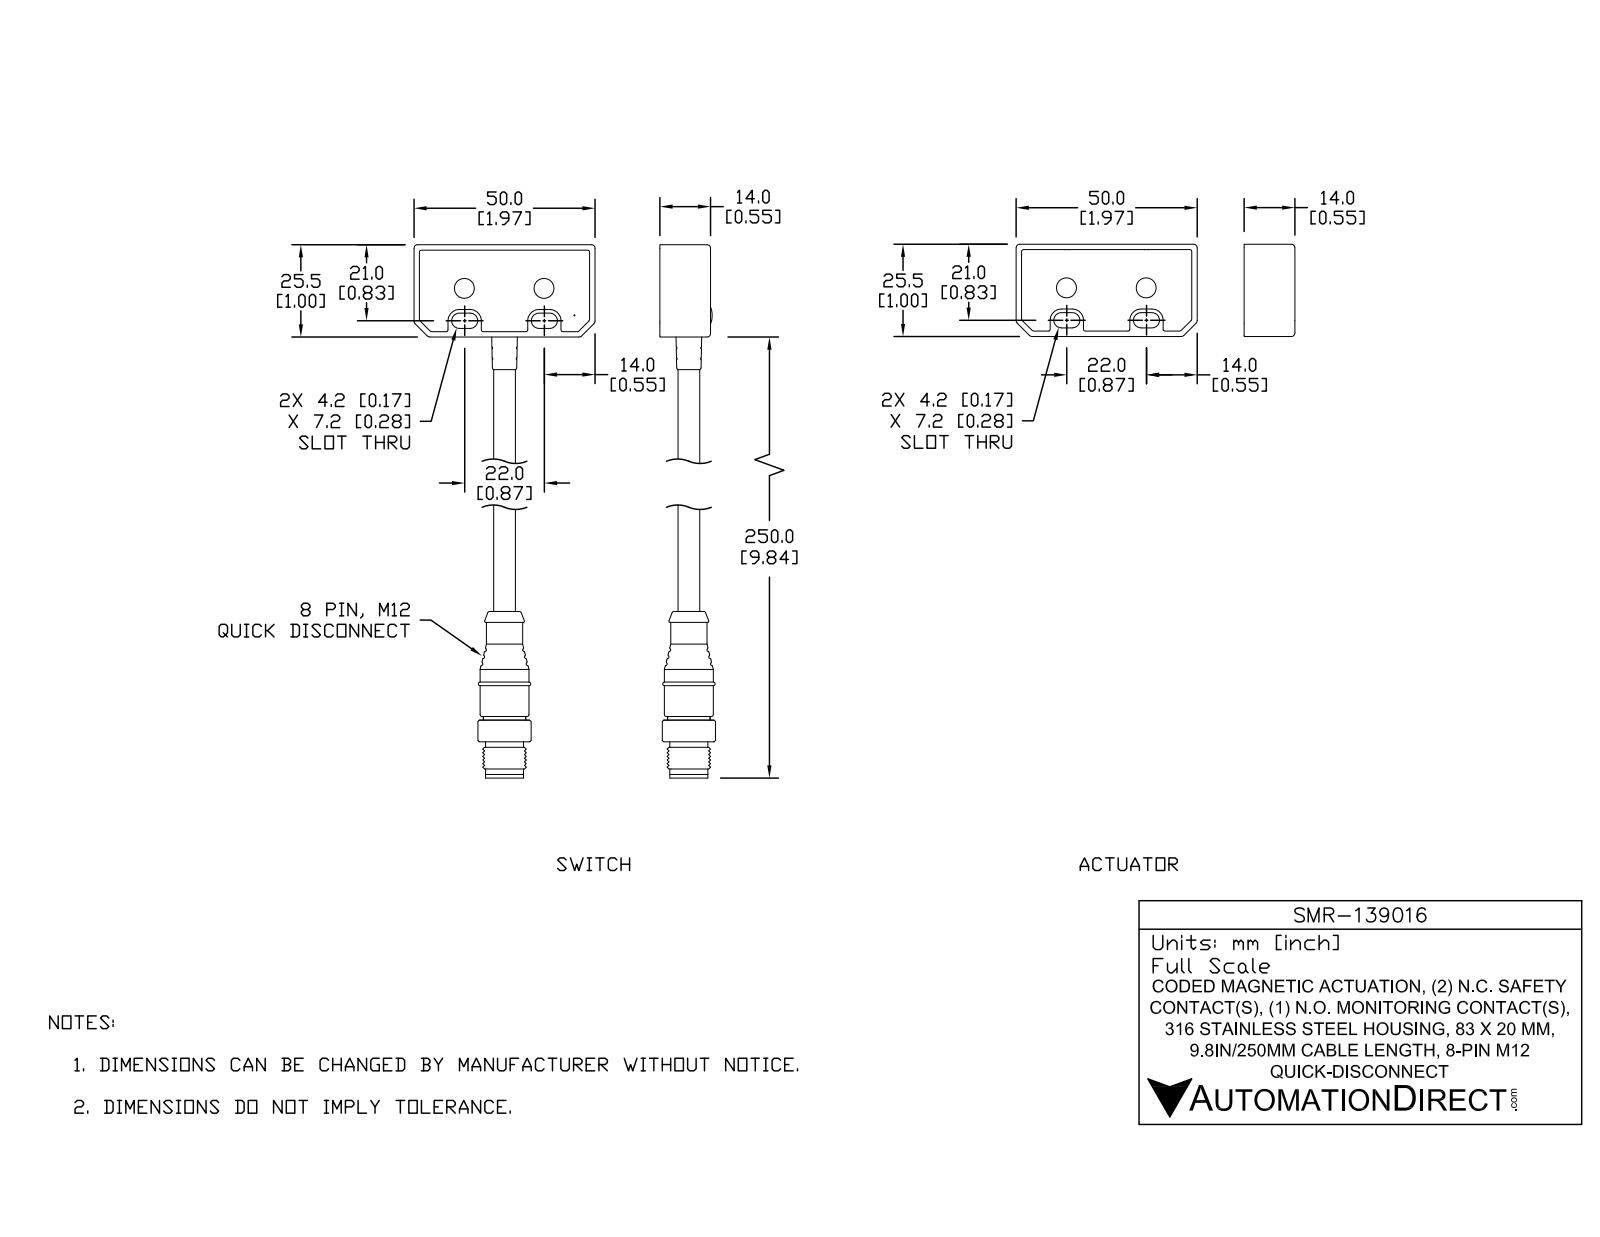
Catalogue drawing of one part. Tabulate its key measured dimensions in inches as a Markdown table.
| quantity | value |
| --- | --- |
| part name | SMR-139016_1; SMR-139016; SMR-139016_2 |
| STEP written by | SolidWorks 2017 (AUTOMOTIVE_DESIGN) |
| units | inches |
| bodies | 4 solids, 201 faces (45 planar, 88 cylindrical, 68 other) |
| overall size | 6.063 × 1.969 × 0.551 |
| volume | 2.184 in³ |
| surface area | 18.53 in² |
| round holes (diameter × count) | 0.287 × 1 |
| round bosses / shafts (diameter × count) | 0.236 × 1 |
| partial cylindrical surfaces (radius × count) | 0.039 × 38, 0.083 × 8, 0.142 × 8, 0.02 × 6 |
| main face-to-face distances | 0.551, 1.004, 1.043, 0.039, 1.969, 2.047, 2.617, 0.177, 0.374, 0.26 |
